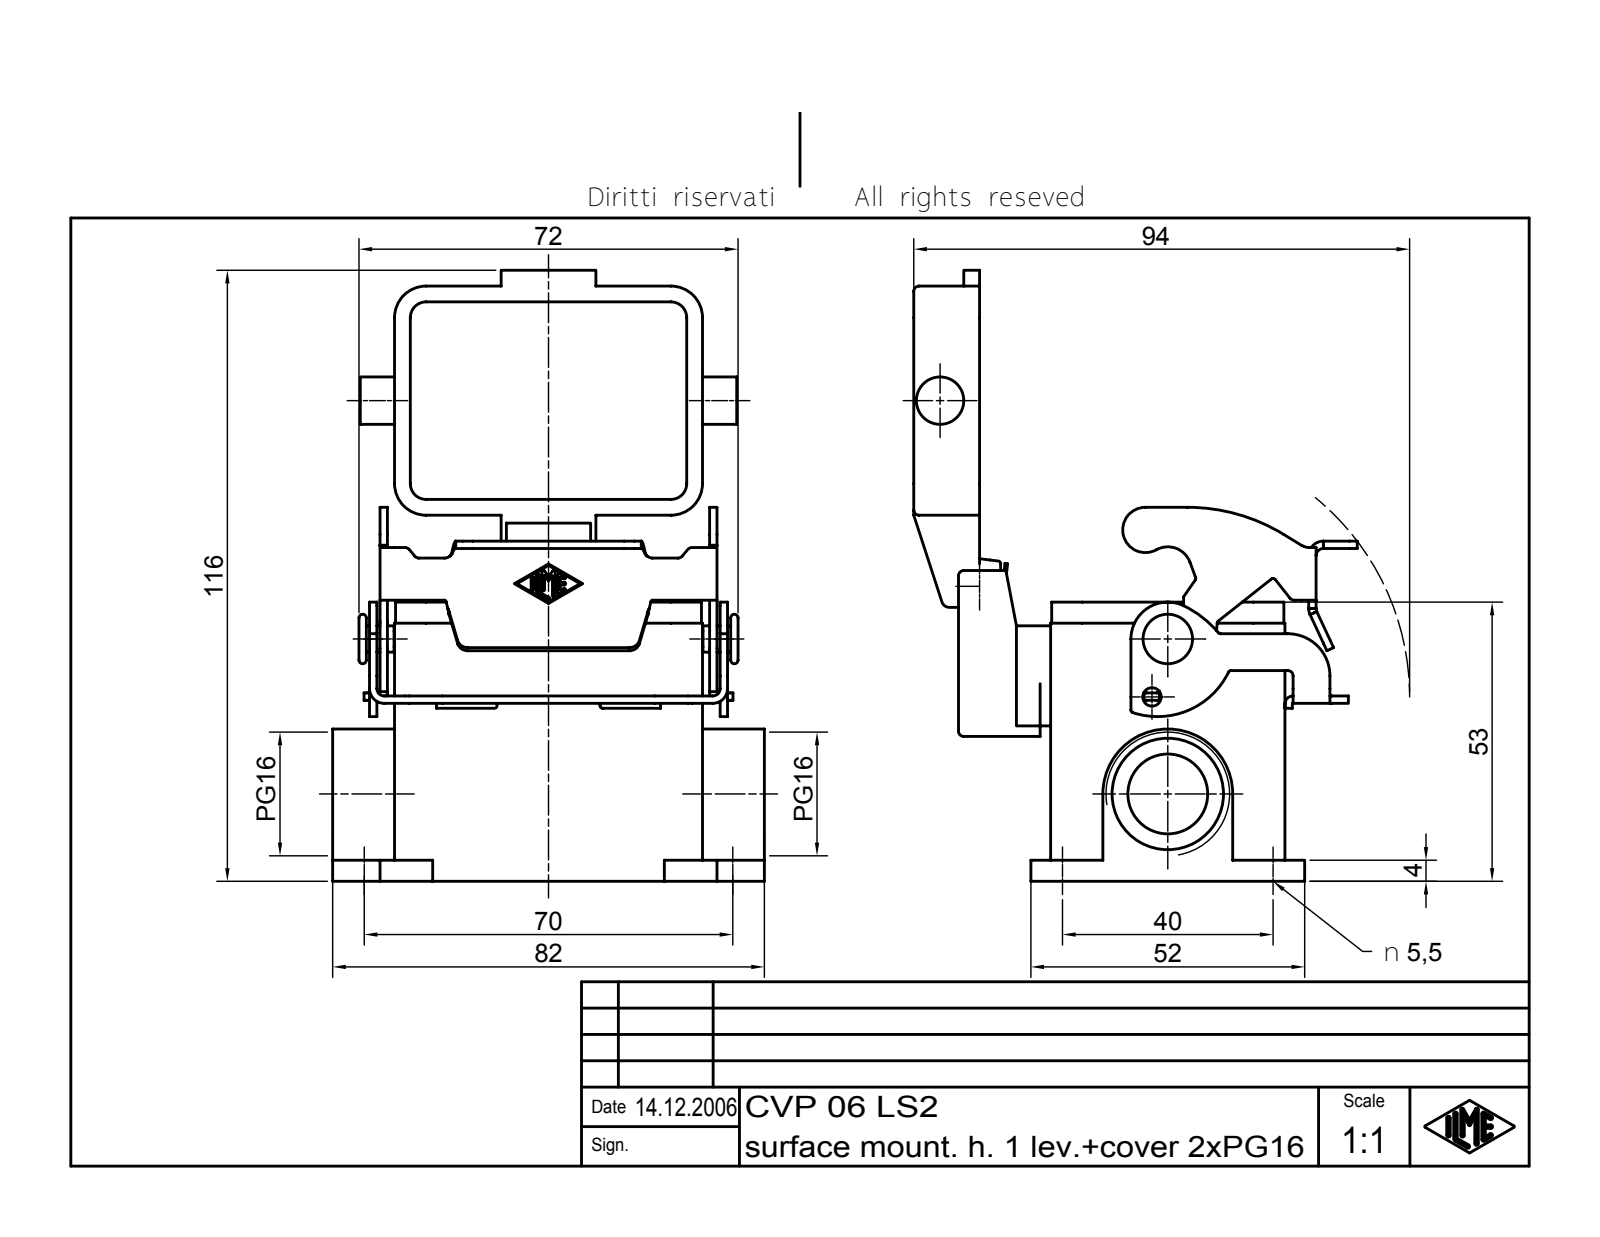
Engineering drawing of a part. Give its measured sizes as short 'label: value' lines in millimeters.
name: CVP 06 LS2
written by: Autodesk Inventor 7 (AUTOMOTIVE_DESIGN)
unit: mm
bodies: 4 solids, 571 faces (221 planar, 185 cylindrical, 165 other)
size: 116 × 84.23 × 82
volume: 93 614 mm³; area: 54 749 mm²
holes: 4× ⌀5.5, 1× ⌀3.5, 1× ⌀4, 1× ⌀15.16, 1× ⌀21.16
bosses: 2× ⌀5, 1× ⌀9, 1× ⌀7, 1× ⌀3.2, 1× ⌀3
rounds: 27× R1, 15× R0.25, 10× R0.5, 10× R1.5, 8× R6, 7× R2, 6× R1.4, 6× R2.8
face distances: 4, 40.5, 26, 44.5, 30, 70.5, 23.5, 2.5, 27.5, 68
hole spacings: 40, 70, 80.62, 18.66
